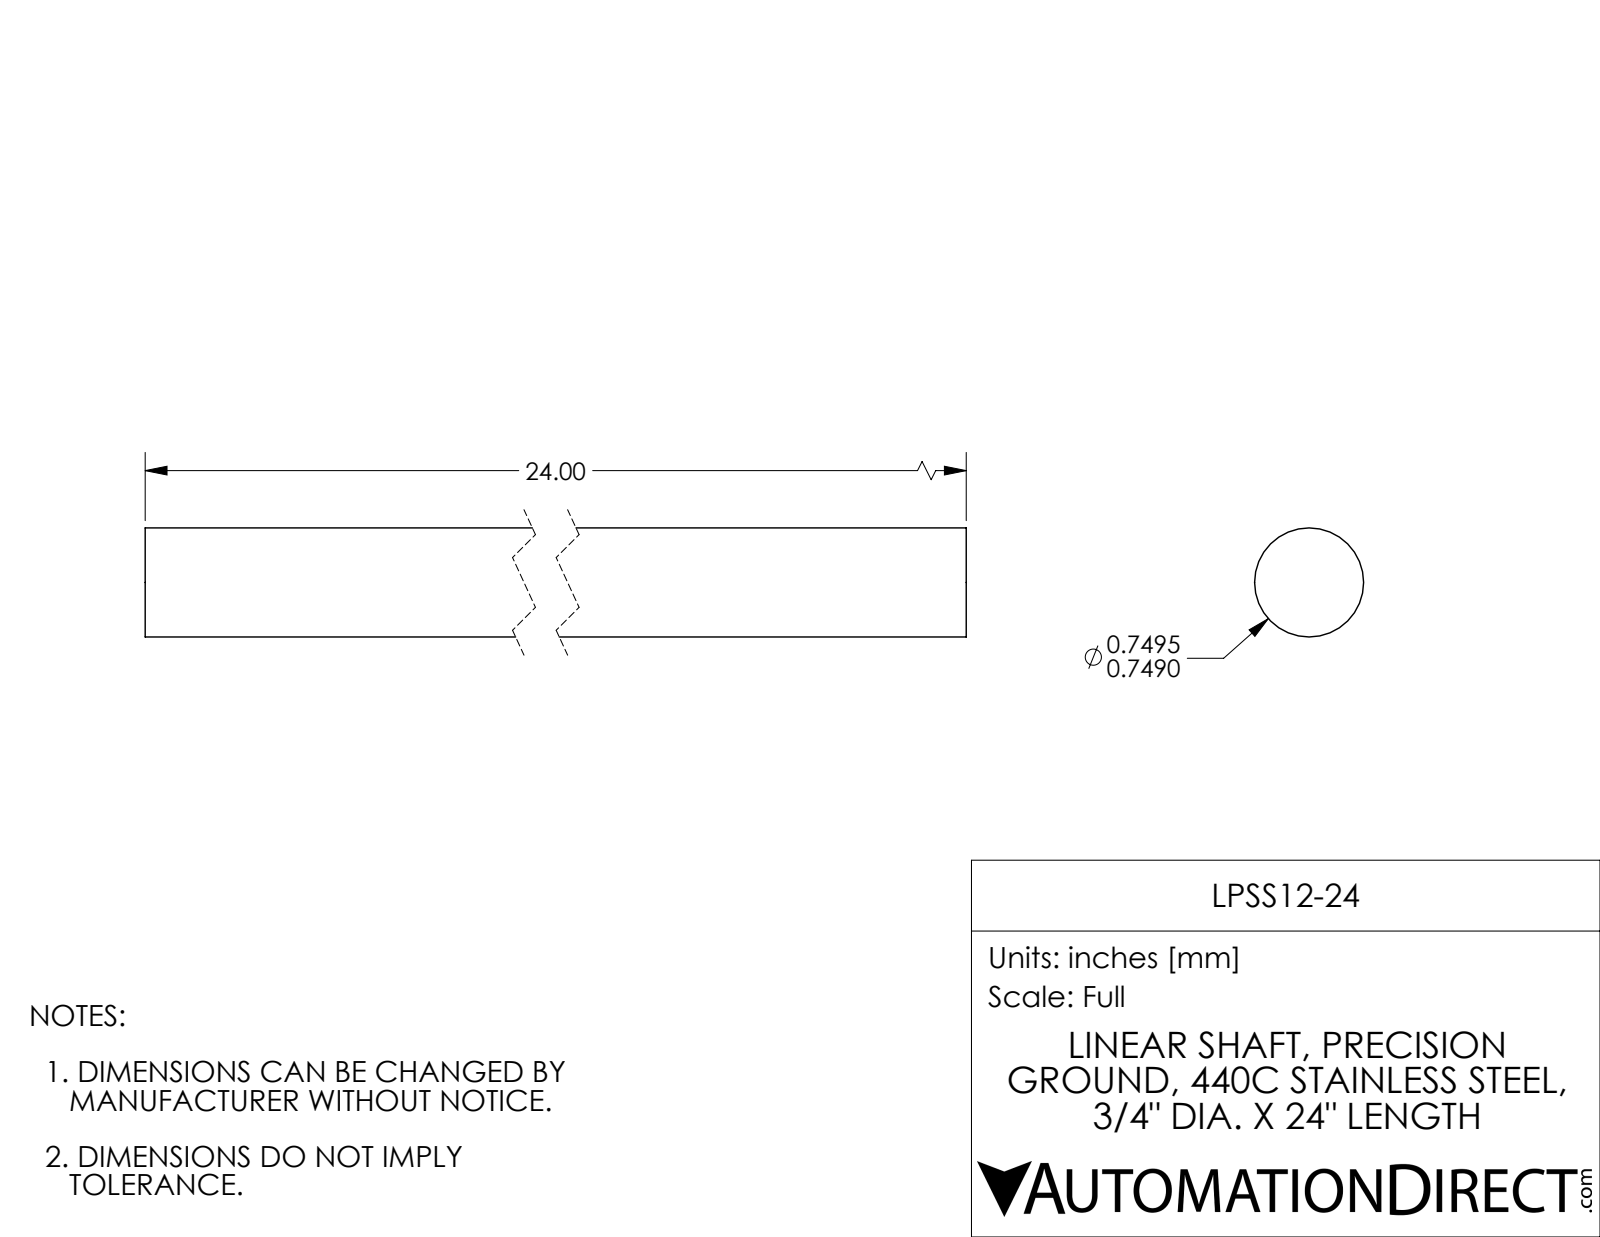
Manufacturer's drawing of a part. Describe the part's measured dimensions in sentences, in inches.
The part is named "LPSS12-24". Its 3-D file was written by "SolidWorks 2017 (AUTOMOTIVE_DESIGN)". It is 1 solid with 4 faces: 2 planar, 2 cylindrical and 0 other. Overall it measures 24 by 0.749 by 0.749 inches. Its volume is 10.59 cubic inches and its surface area 57.39 square inches. Round bosses or shafts: 1 of diameter 0.75. The main face-to-face distances are 24.
